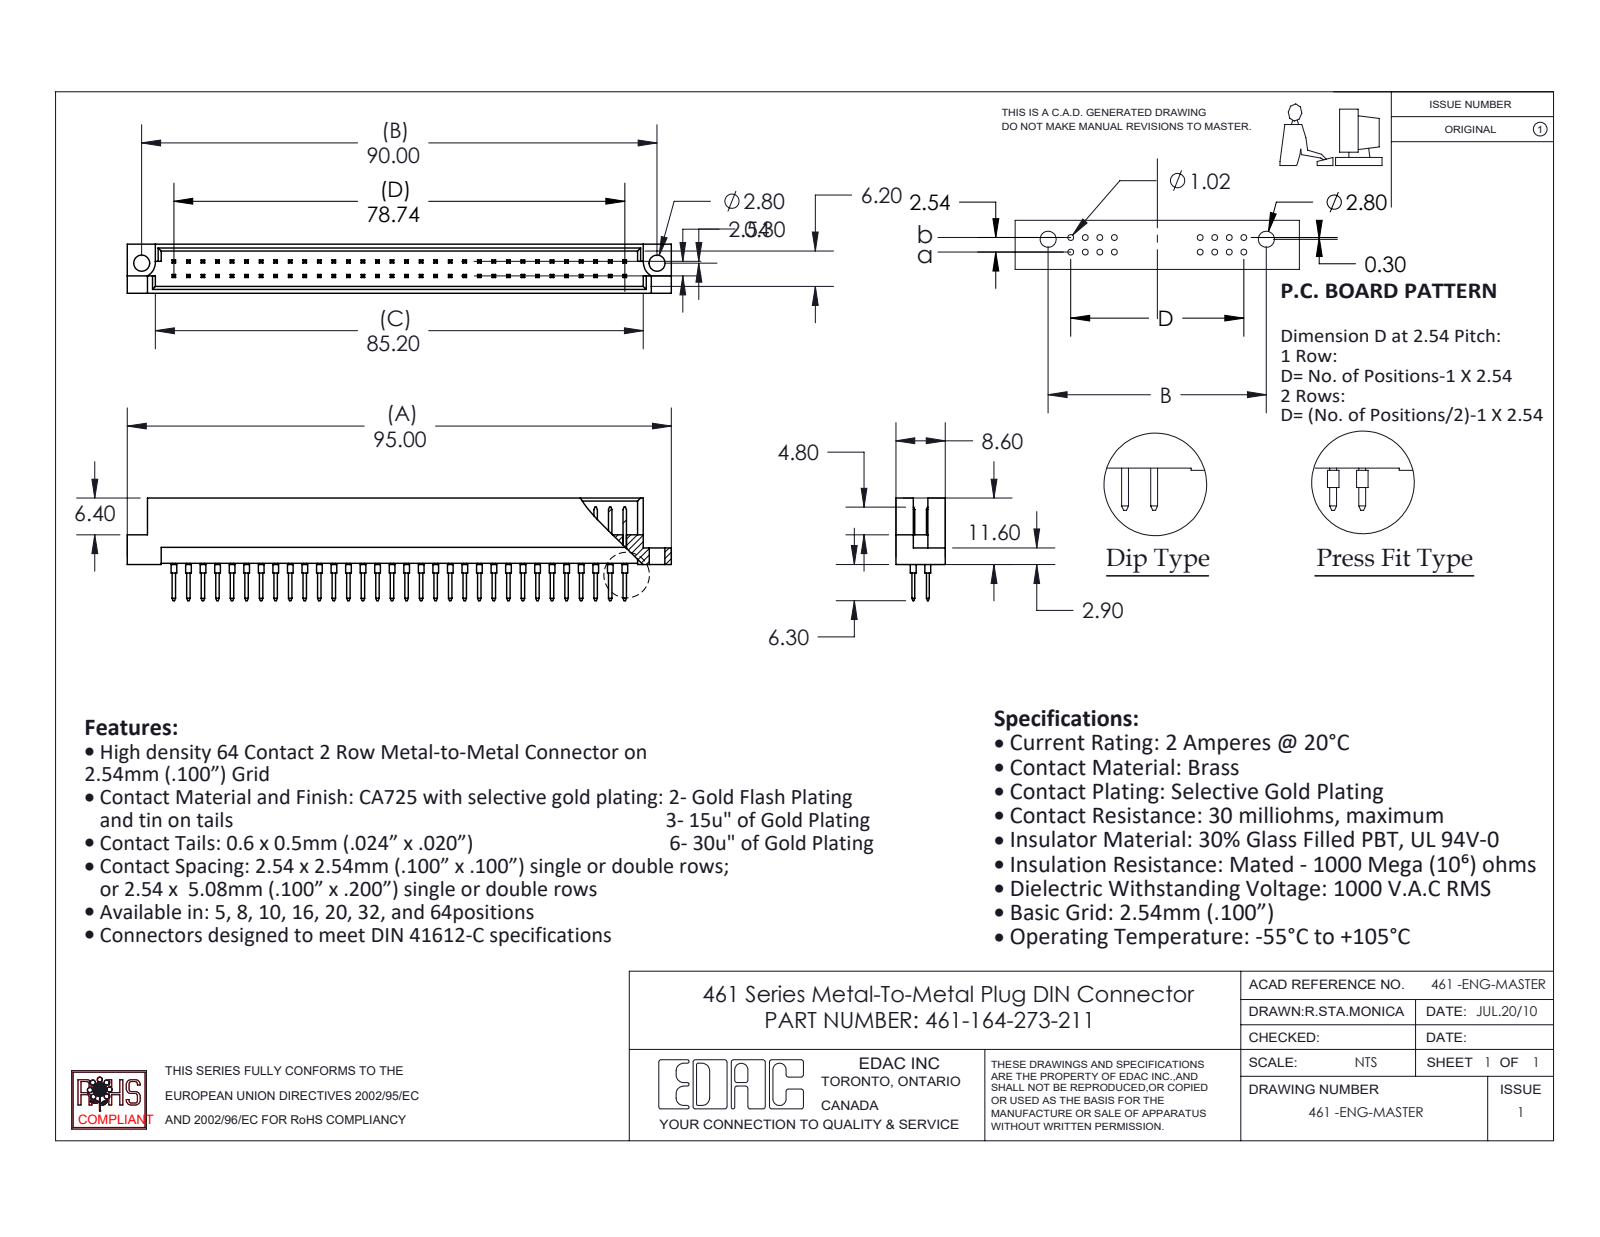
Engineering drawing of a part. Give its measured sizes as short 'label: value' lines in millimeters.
name: 461-290_73; 461 Part_64; 461-164-273-211
written by: SolidWorks 2020 (CONFIG_CONTROL_DESIGN)
unit: mm
bodies: 65 solids, 1713 faces (1578 planar, 135 cylindrical, 0 other)
size: 95 × 17.9 × 8.6
volume: 5 009 mm³; area: 8 094 mm²
holes: 2× ⌀2.8
bosses: 64× ⌀1
rounds: 2× R2.8
face distances: 1.2, 7.4, 2.54, 8.6, 3.28, 5.32, 2.08, 4.12, 2.78, 5.82
hole spacings: 90
